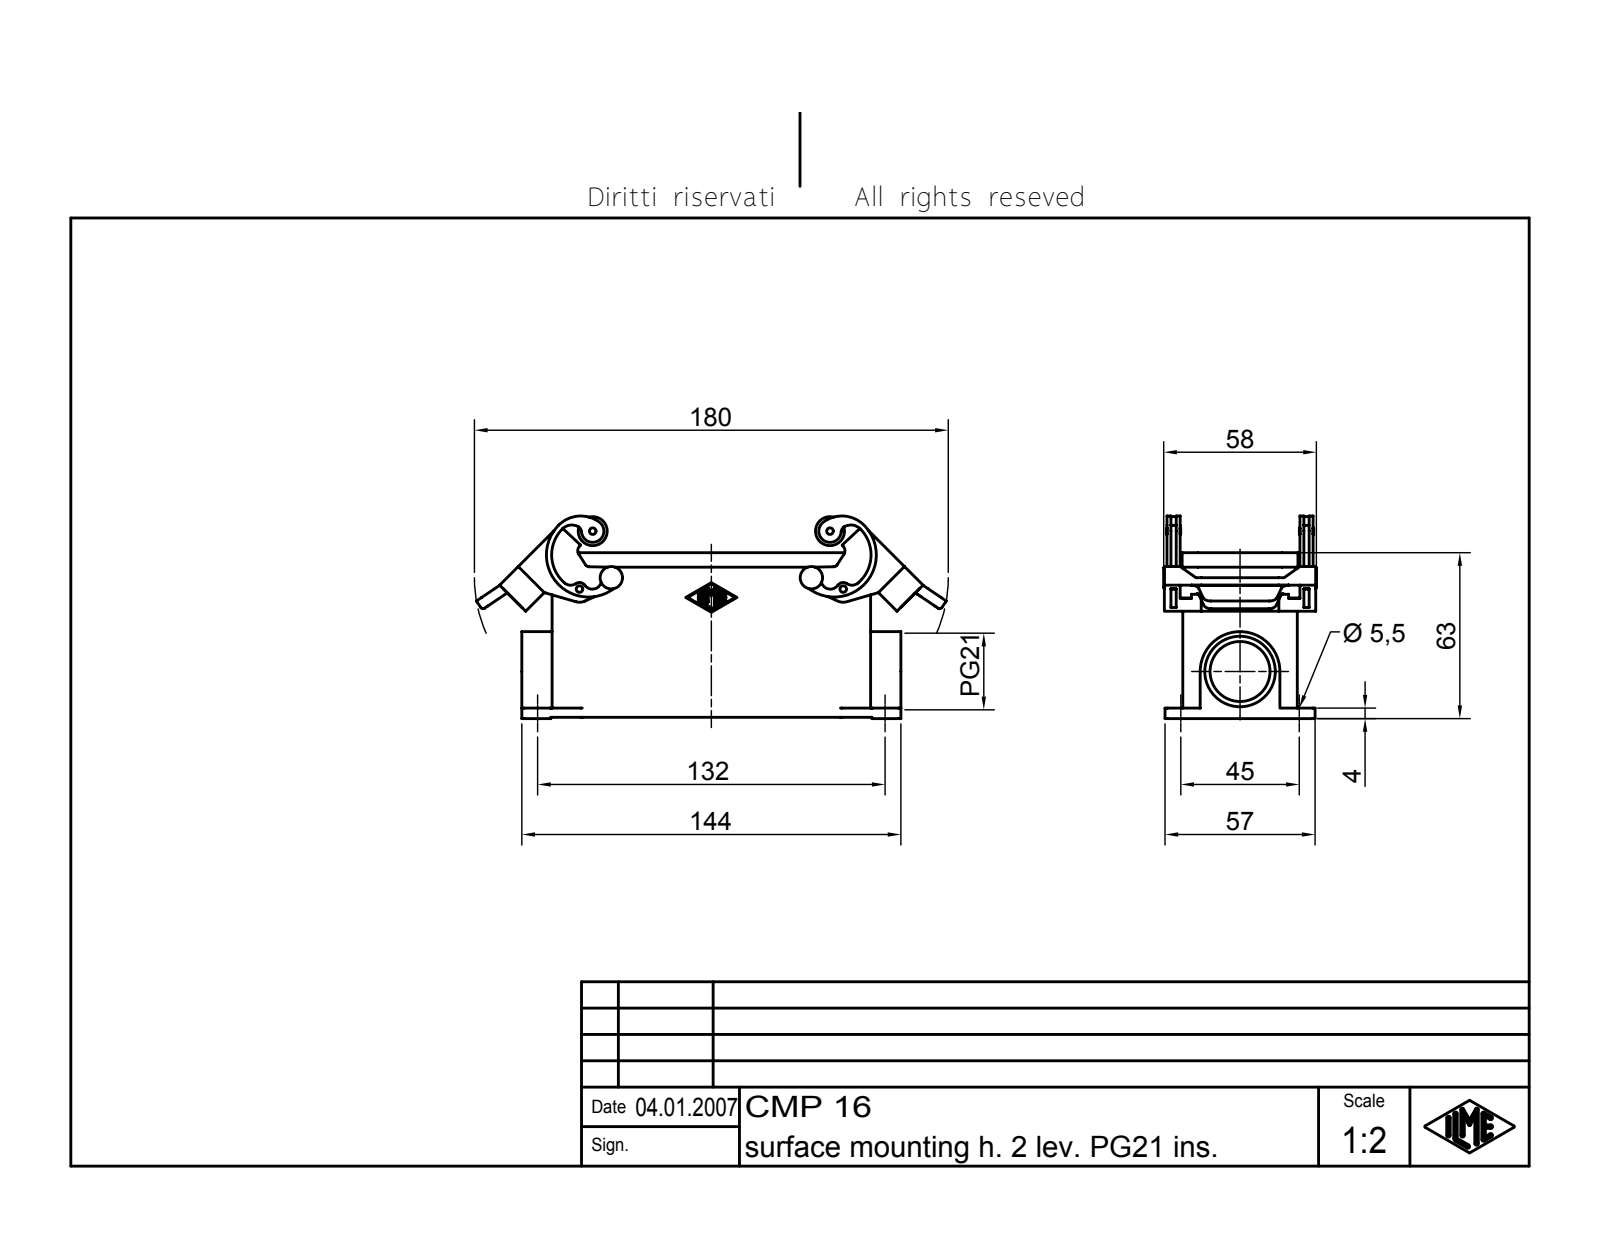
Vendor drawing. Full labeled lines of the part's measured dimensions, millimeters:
Part name (STEP PRODUCT): CMP 16
STEP written by: Autodesk Inventor 7 (AUTOMOTIVE_DESIGN)
Units: millimetres
Bodies: 1 solid, 749 faces (191 planar, 205 cylindrical, 353 other)
Overall size (bounding box): 178.49 × 76.94 × 58
Volume: 120 760 mm³ · Surface area: 71 190 mm²
Round holes (diameter × count): ⌀2 ×4, ⌀5.5 ×4, ⌀2.5 ×2, ⌀22.78 ×1, ⌀26.78 ×1
Round bosses / shafts (diameter × count): ⌀11 ×2, ⌀5 ×2, ⌀3 ×2
Partial cylindrical surfaces — rounded edges, fillets, slot ends (radius × count): R1 ×20, R0.38 ×14, R3 ×12, R6 ×8, R2.5 ×6, R1.5 ×4, R2 ×4, R3.5 ×4
Main face-to-face distances: 3, 40.5, 43.5, 37.5, 3.5, 4, 0.75, 50.5, 40.75, 3.75
Hole centre spacings: 22.56, 45, 97.67, 132, 139.46, 90.14, 100.18
